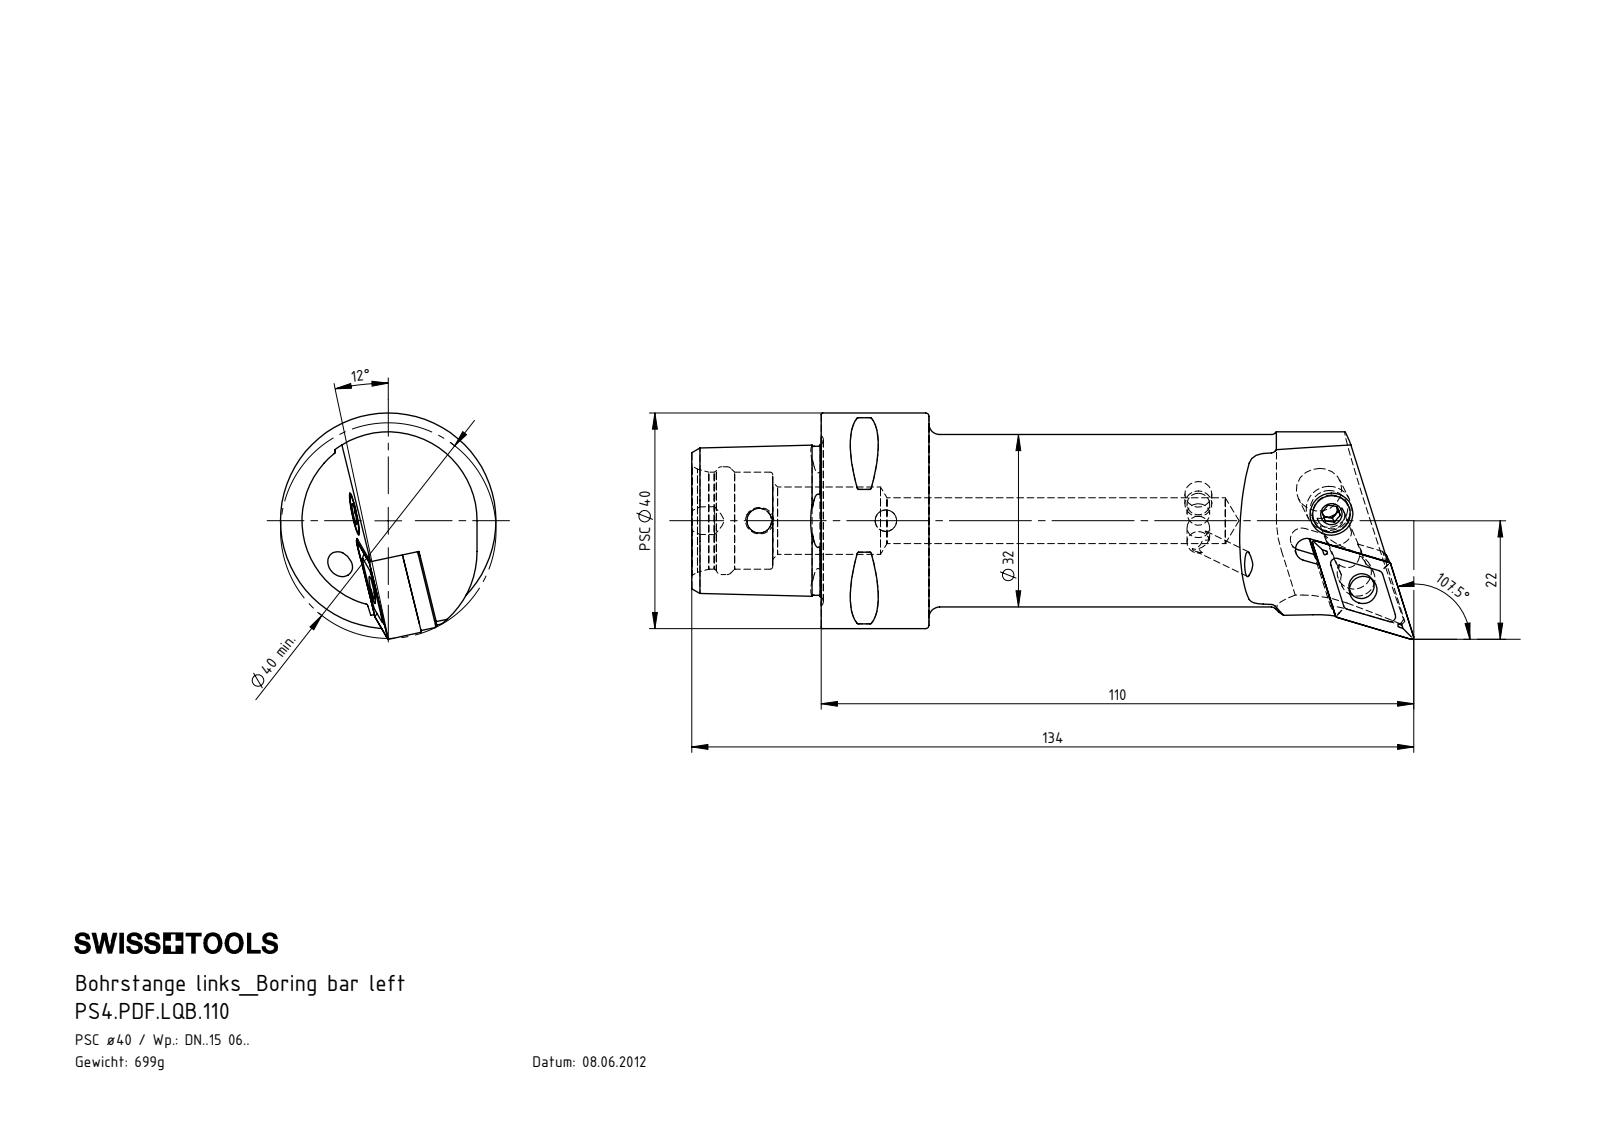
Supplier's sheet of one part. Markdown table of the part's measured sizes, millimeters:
| quantity | value |
| --- | --- |
| part name | WCD-ER4.101.017_A; WDF-ER2.101.003_A; KVT_MB_600_050; PS4-PDF.LQB.110_A (+4 more) |
| STEP written by | SolidWorks 2017 (AUTOMOTIVE_DESIGN) |
| units | millimeters |
| bodies | 8 solids, 364 faces (92 planar, 88 cylindrical, 184 other) |
| overall size | 134 × 42 × 40 |
| volume | 89 983 mm³ |
| surface area | 22 710 mm² |
| round holes (diameter × count) | 4 × 2, 4.2 × 2, 4.6 × 1, 5.16 × 1, 6.4 × 1, 7 × 1, 8.4 × 1, 8.5 × 1, 12.5 × 1, 18 × 1, 20 × 1 |
| round bosses / shafts (diameter × count) | 40 × 1, 32 × 1, 8 × 1, 7.9 × 1, 6.4 × 1, 5 × 1, 4.7 × 1, 3.55 × 1 |
| partial cylindrical surfaces (radius × count) | 0.3 × 8, 0.4 × 4, 1 × 4, 2.5 × 2, 3 × 2, 2.1 × 1, 2.35 × 1, 2.8 × 1 |
| main face-to-face distances | 6.05, 12.7, 20, 24, 44, 9.22, 15.52, 3.18, 9.23, 12.28 |
| hole center spacings | 15.59, 23.5 |
